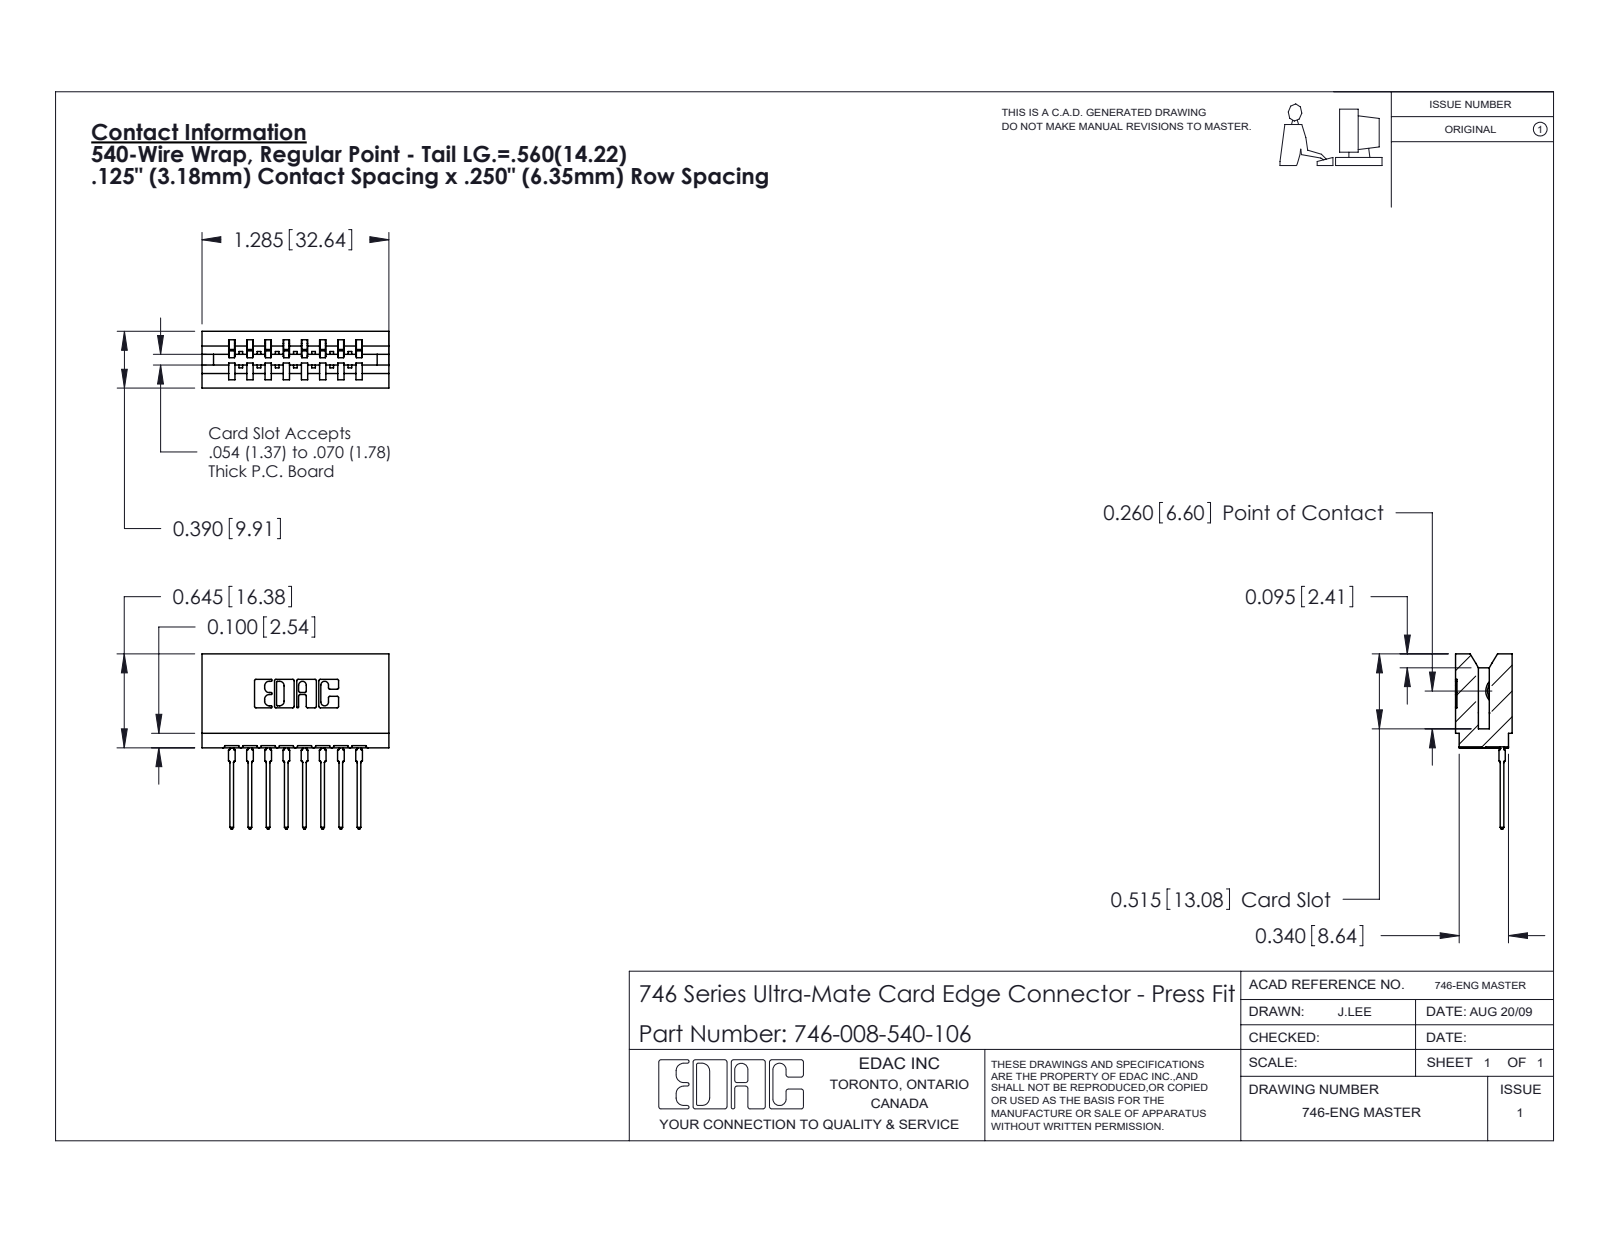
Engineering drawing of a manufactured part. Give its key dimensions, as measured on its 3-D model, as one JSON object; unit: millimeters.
{"part_name": "746 Part_.515 Slot Depth - 06; 746-008-540-106; 746-292-001_540", "step_written_by": "SolidWorks 2020 (CONFIG_CONTROL_DESIGN)", "units": "millimeters", "bodies": {"solids": 9, "faces": 962, "planar": 560, "cylindrical": 194, "other": 208}, "overall_size": [32.6, 30.6, 9.9], "volume_mm3": 3640, "surface_area_mm2": 4932, "partial_cylinders_radius": [[0.3, 22], [0.5, 16], [0.4, 9], [0.2, 6], [0.8, 6], [0.1, 4], [0.3, 4], [0.7, 3]], "face_to_face_distances": [6.4, 3.2, 12.7, 1.1, 8.5, 1.4, 7.4, 9.5, 5.3, 3.2]}
